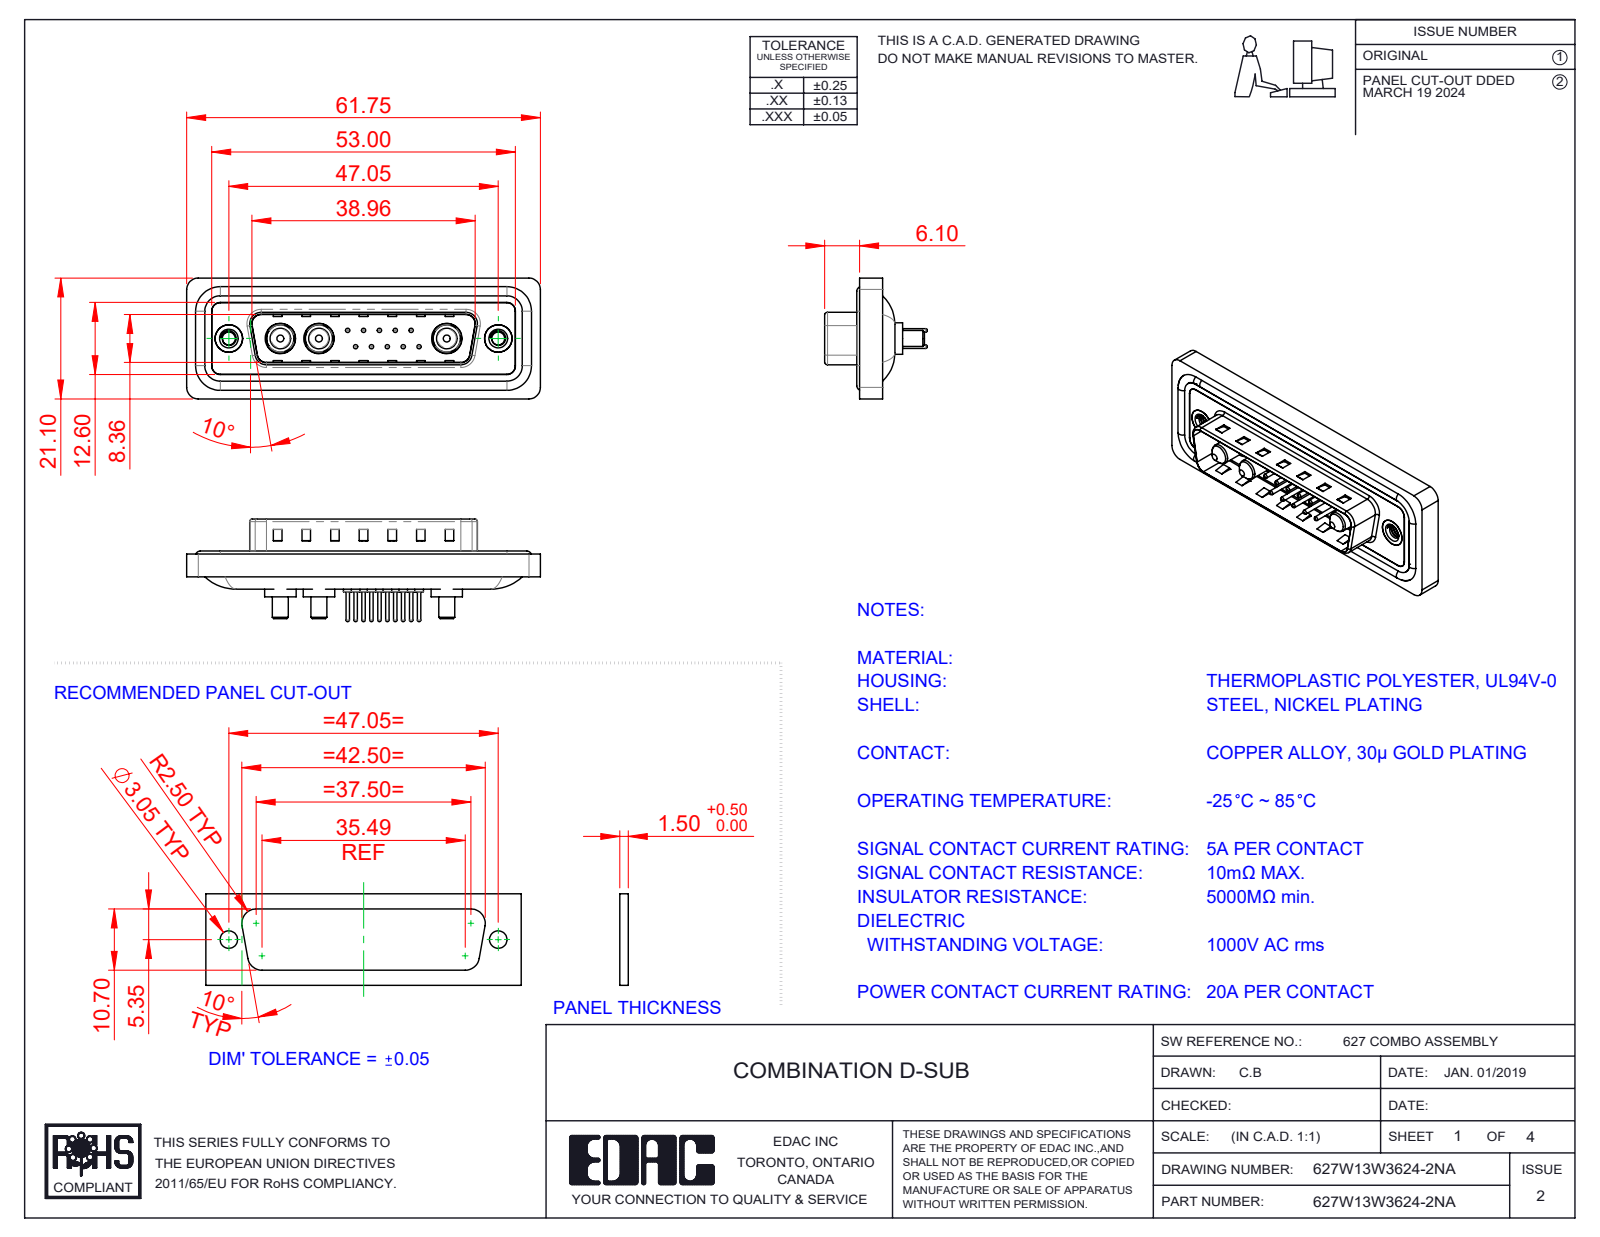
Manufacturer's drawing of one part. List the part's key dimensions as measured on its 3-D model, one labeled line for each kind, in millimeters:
Part name (STEP PRODUCT): 627Combo Waterproof Housing_25 Contacts; 627Combo Shell Front_25 Contacts; 627Combo Threaded Rivet_A; 627Combo Housing_13W3 (+5 more)
STEP written by: SolidWorks 2023 (CONFIG_CONTROL_DESIGN)
Units: millimetres
Bodies: 23 solids, 968 faces (309 planar, 387 cylindrical, 272 other)
Overall size (bounding box): 61.75 × 21.1 × 17.9
Volume: 7 337 mm³ · Surface area: 11 872 mm²
Round holes (diameter × count): ⌀0.75 ×10, ⌀1.6 ×10, ⌀2 ×10, ⌀4.85 ×3, ⌀5.3 ×3, ⌀2.26 ×2, ⌀4 ×2, ⌀4.8 ×2, ⌀5 ×2
Round bosses / shafts (diameter × count): ⌀1.5 ×10, ⌀0.6 ×10, ⌀1.6 ×4, ⌀5.5 ×3, ⌀5.2 ×3, ⌀4.75 ×3, ⌀3.75 ×3, ⌀3.6 ×3
Partial cylindrical surfaces — rounded edges, fillets, slot ends (radius × count): R1.5 ×22, R2 ×18, R0.5 ×8, R1.6 ×8, R0.25 ×4, R0.6 ×4, R0.65 ×4, R0.9 ×4
Main face-to-face distances: 0.4, 1.5, 1.1, 1.6, 0.5, 3.1, 2.9, 0.82, 9.58, 4.1
Hole centre spacings: 3.16, 2.77, 5.04, 5.54, 7.49, 5.03, 8.31, 10.11
